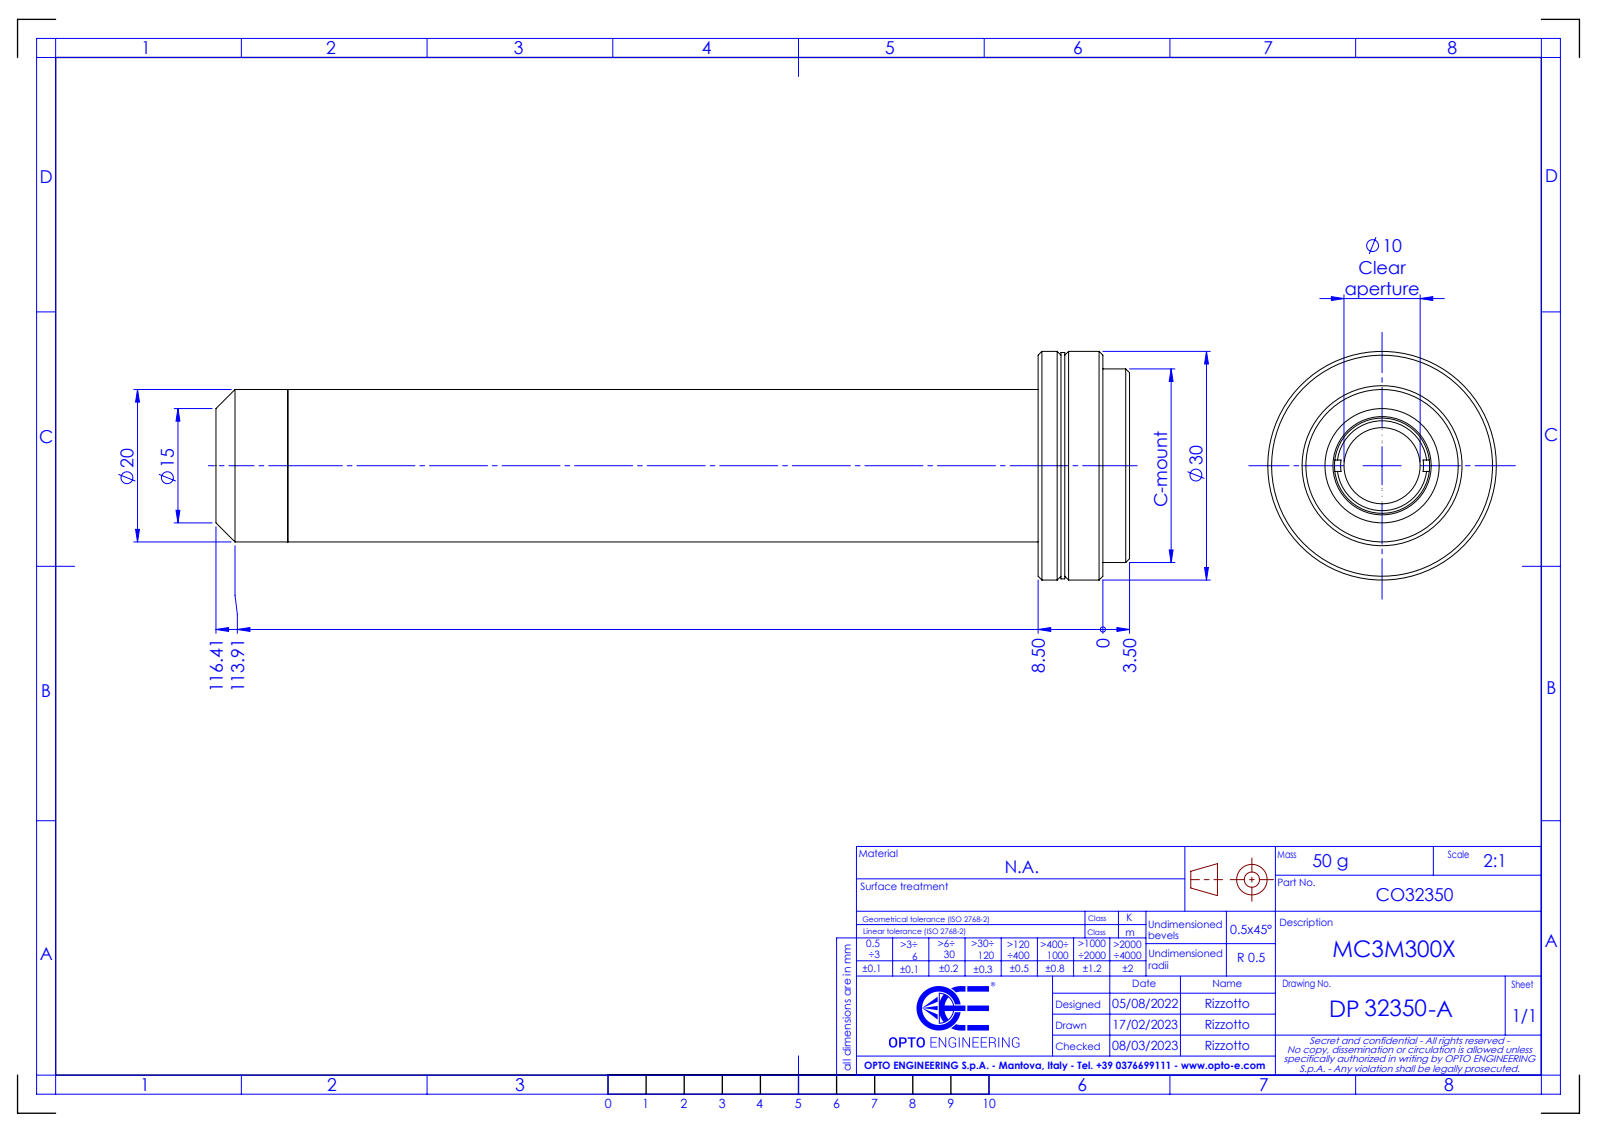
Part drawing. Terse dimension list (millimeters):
name: DP32350-A_MC3M300X
written by: SolidWorks 2021 (CONFIG_CONTROL_DESIGN)
unit: mm
bodies: 0 solids, 66 faces (16 planar, 24 cylindrical, 26 other)
size: 119.91 × 30 × 30
holes: 1× ⌀10, 1× ⌀12.5, 1× ⌀17.5, 1× ⌀18, 1× ⌀20
bosses: 1× ⌀30, 1× ⌀29.7, 1× ⌀25.4
face distances: 8.5, 3.5, 5, 3, 0.5, 5.5, 12, 9, 98.48, 101.48
